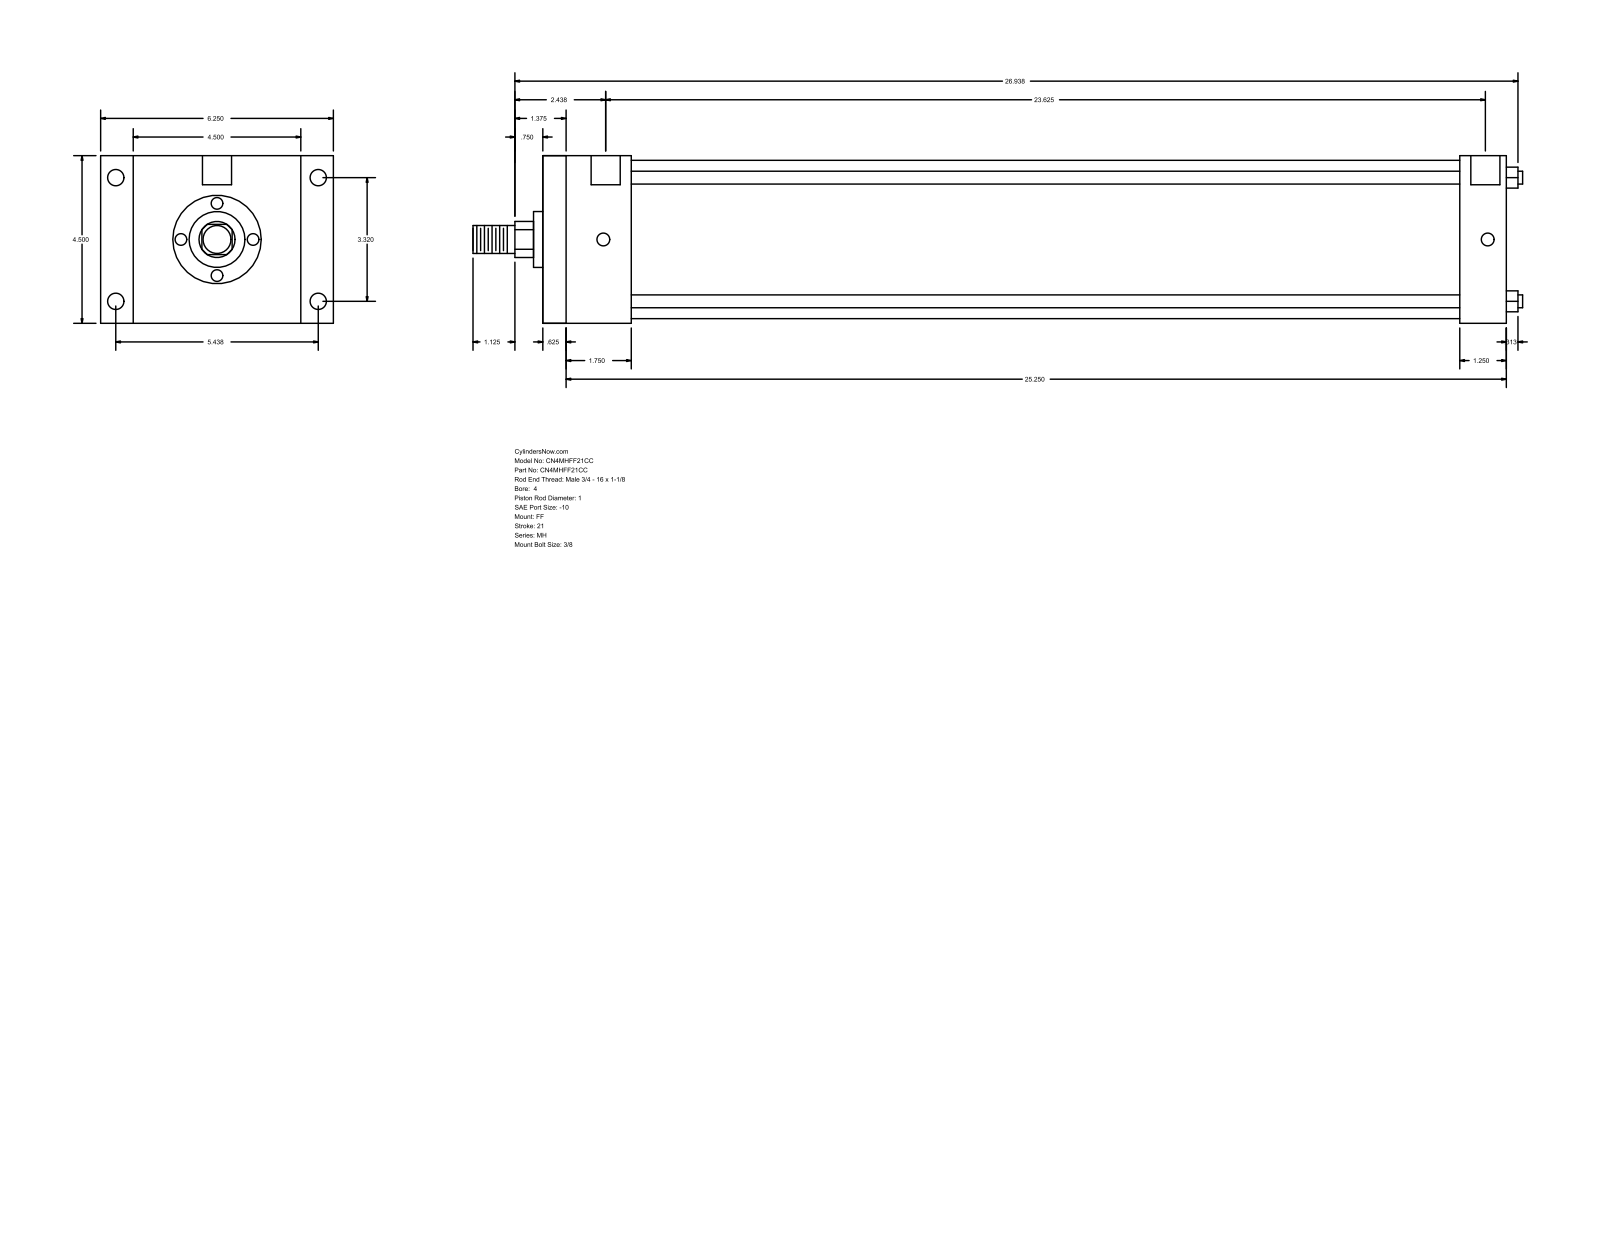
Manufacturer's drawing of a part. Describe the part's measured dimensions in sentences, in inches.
The part is named "MH_FF__0400_1". Its 3-D file was written by "GSSL Pune (CONFIG_CONTROL_DESIGN)". It is 0 solids with 92 faces: 64 planar, 28 cylindrical and 0 other. Overall it measures 28.187 by 6.25 by 4.5 inches. Round holes: 4 of diameter 0.344, 4 of diameter 0.438, 2 of diameter 0.781. Round bosses or shafts: 4 of diameter 0.345, 1 of diameter 4.25, 1 of diameter 1.5, 1 of diameter 1, 1 of diameter 0.75. Partial cylindrical surfaces (rounded edges, fillets, slot ends): 1 of radius 0.484. The main face-to-face distances are 4.5, 25.875, 0.625, 25.25, 2.375, 1.75, 23.5, 24.625, 24, 22.25. The hole center spacings are 3.32, 5.438, 6.371, 23.75, 0.062, 0.063, 23.625, 23.687.
